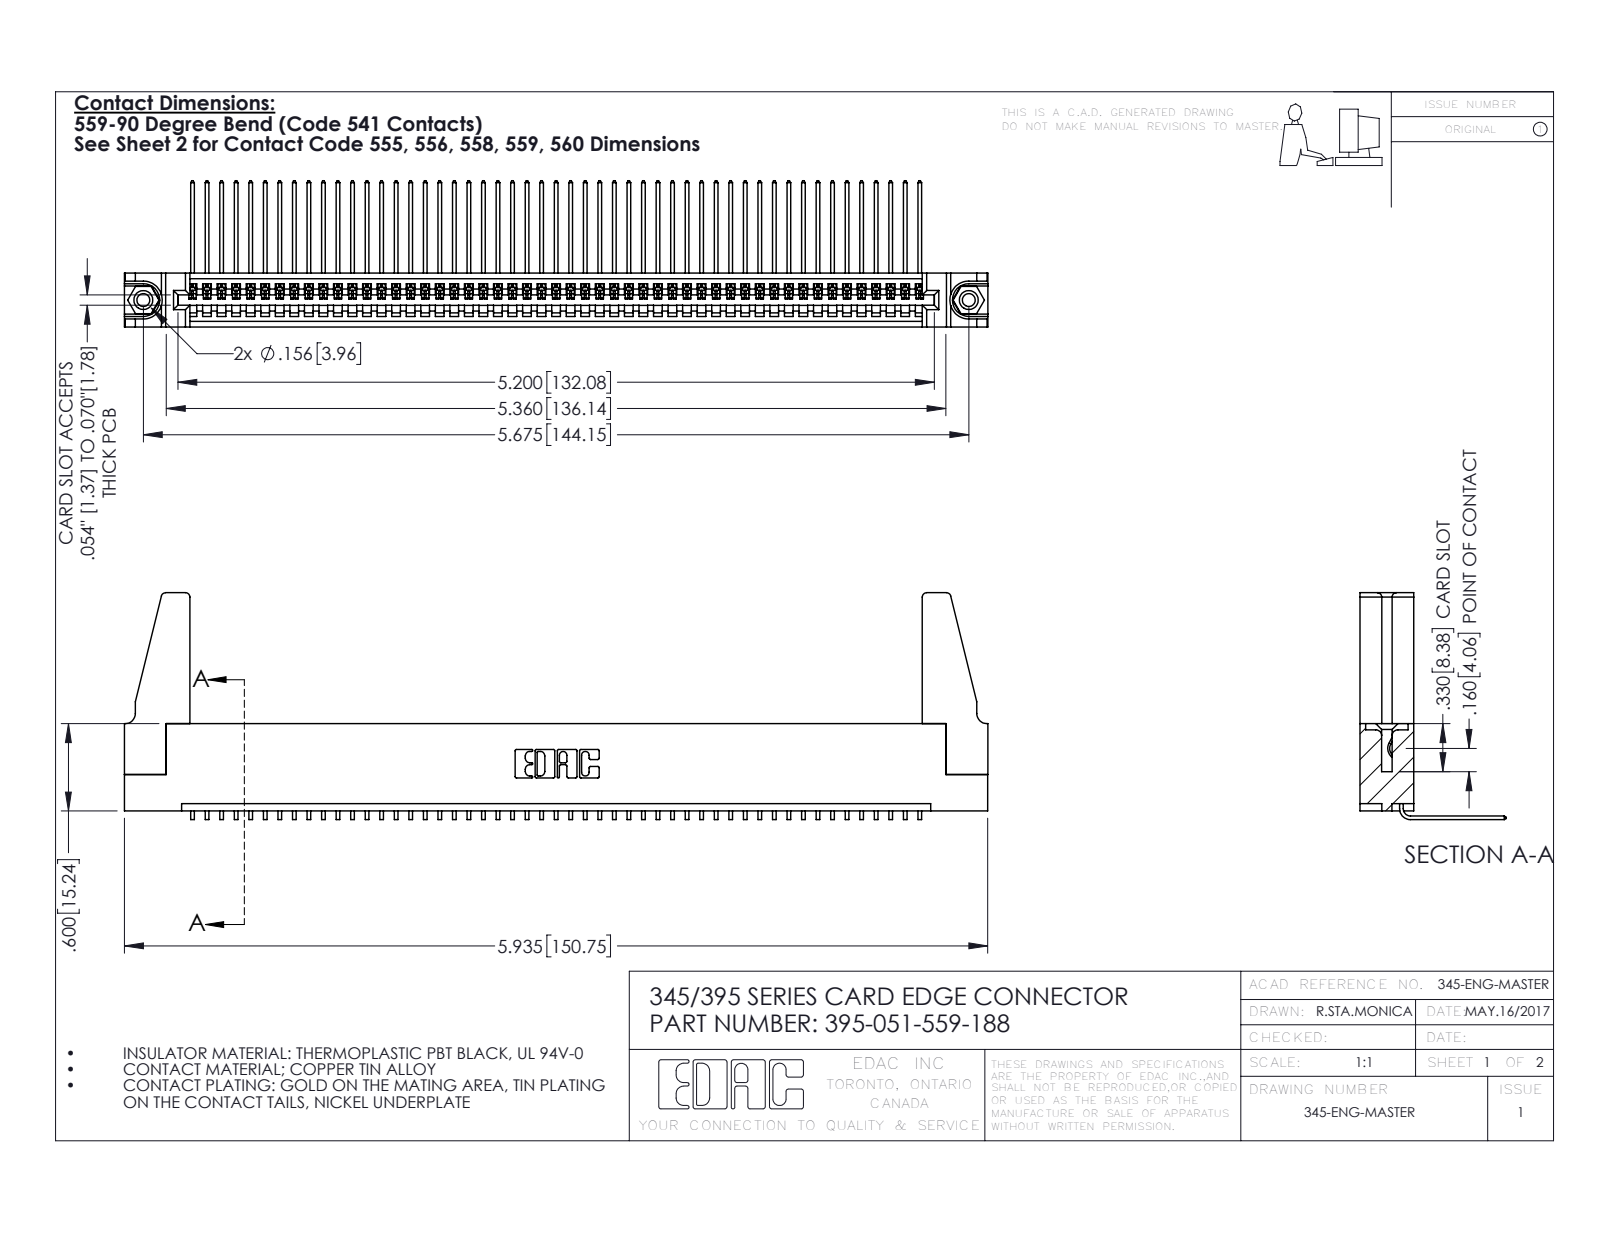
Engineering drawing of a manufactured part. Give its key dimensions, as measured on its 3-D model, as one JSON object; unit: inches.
{"part_name": "395-051-559-188; 345 Part_Flush Mounting Lugs - 0.156 Dia-TH; 345-220-078_345-220-088; 345-292-001_558 559 Tail - 1 (+1 more)", "step_written_by": "SolidWorks 2016 (CONFIG_CONTROL_DESIGN)", "units": "inches", "bodies": {"solids": 56, "faces": 3310, "planar": 2294, "cylindrical": 1000, "other": 16}, "overall_size": [5.936, 1.559, 1.005], "volume_in3": 1.087, "surface_area_in2": 36.59, "round_holes": [[0.089, 2], [0.125, 2], [0.156, 2], [0.064, 1]], "round_bosses_or_shafts": [[0.155, 2]], "partial_cylinders_radius": [[0.006, 102], [0.01, 22], [0.03, 8], [0.007, 6], [0.031, 6], [0.026, 3], [0.031, 2], [0.04, 2]], "face_to_face_distances": [0.072, 0.298, 0.37, 0.2, 0.098, 0.272, 0.025, 0.225, 0.149, 0.072], "hole_center_spacings": [0.27, 5.439, 5.675]}
